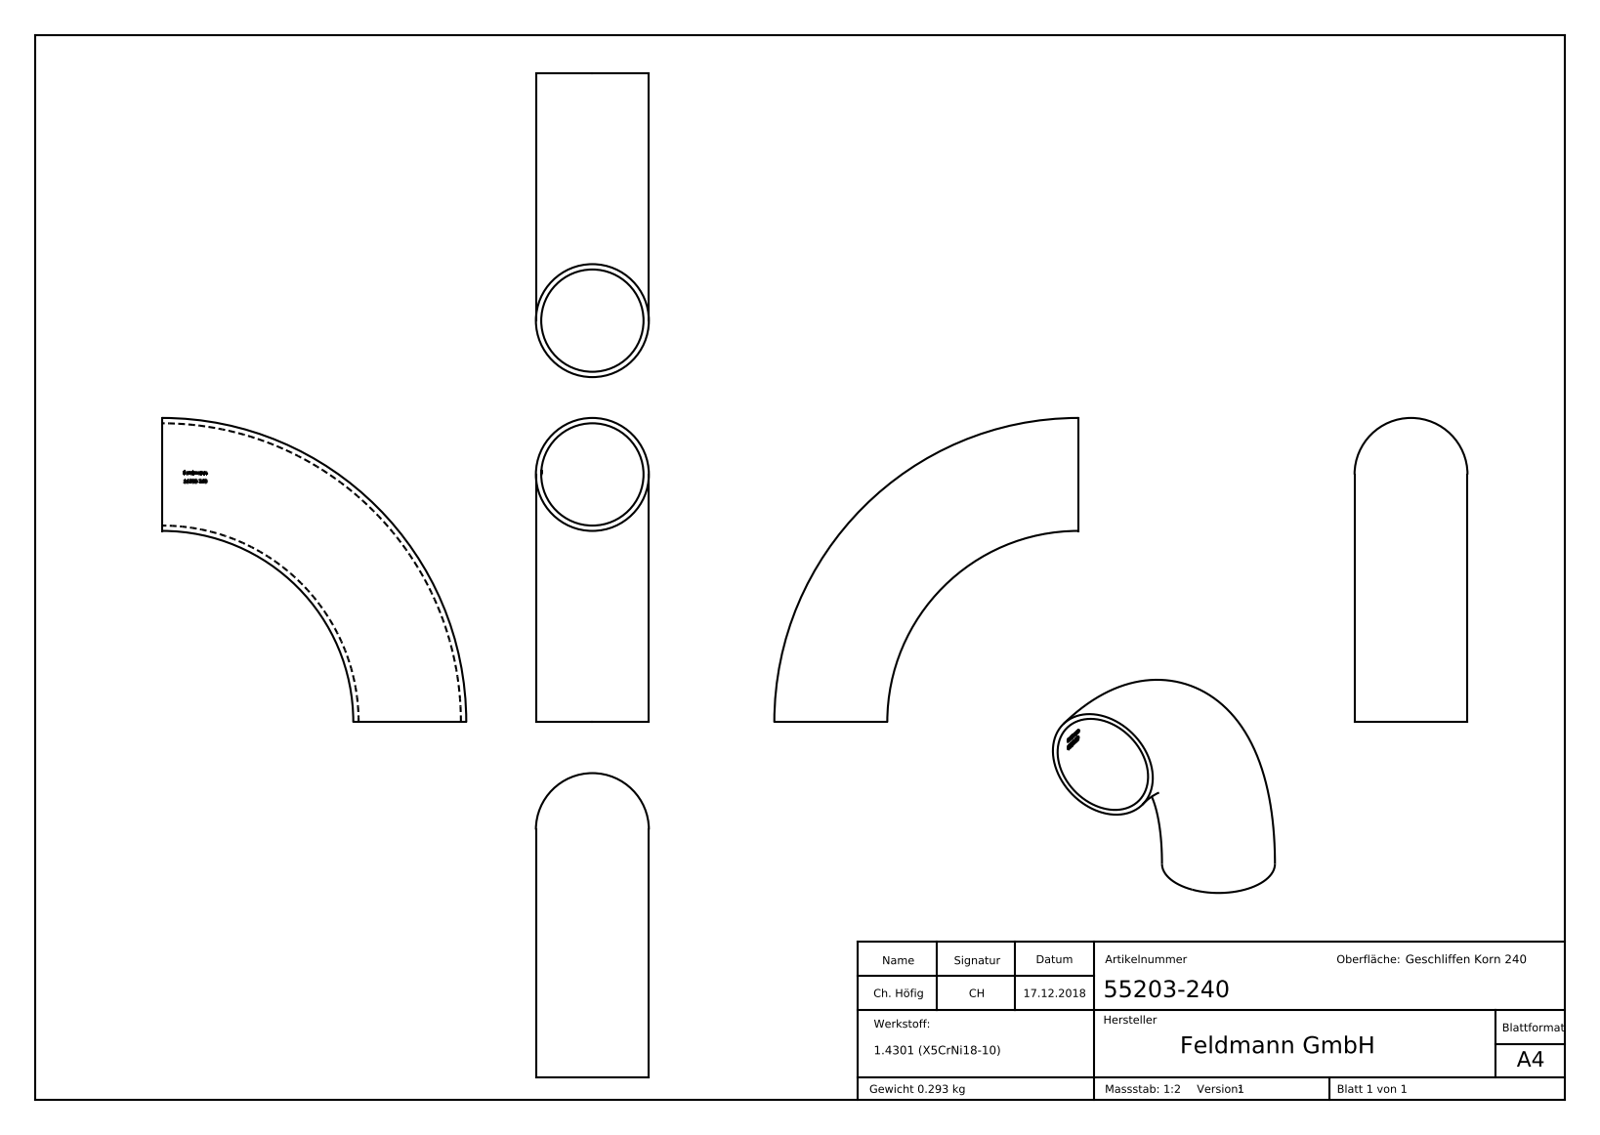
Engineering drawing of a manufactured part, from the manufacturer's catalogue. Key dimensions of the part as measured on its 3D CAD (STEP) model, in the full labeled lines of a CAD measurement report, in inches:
Part name (STEP PRODUCT): 55203-240
STEP written by: SolidWorks 2015 (CONFIG_CONTROL_DESIGN)
Units: inches
Bodies: 1 solid, 235 faces (100 planar, 0 cylindrical, 135 other)
Overall size (bounding box): 4.496 × 4.496 × 1.669
Volume: 2.263 in³ · Surface area: 58.28 in²
Main face-to-face distances: 0.015, 0.117, 0.052, 0.161, 0.044, 0.144, 0.129, 0.08, 0.035, 0.132
